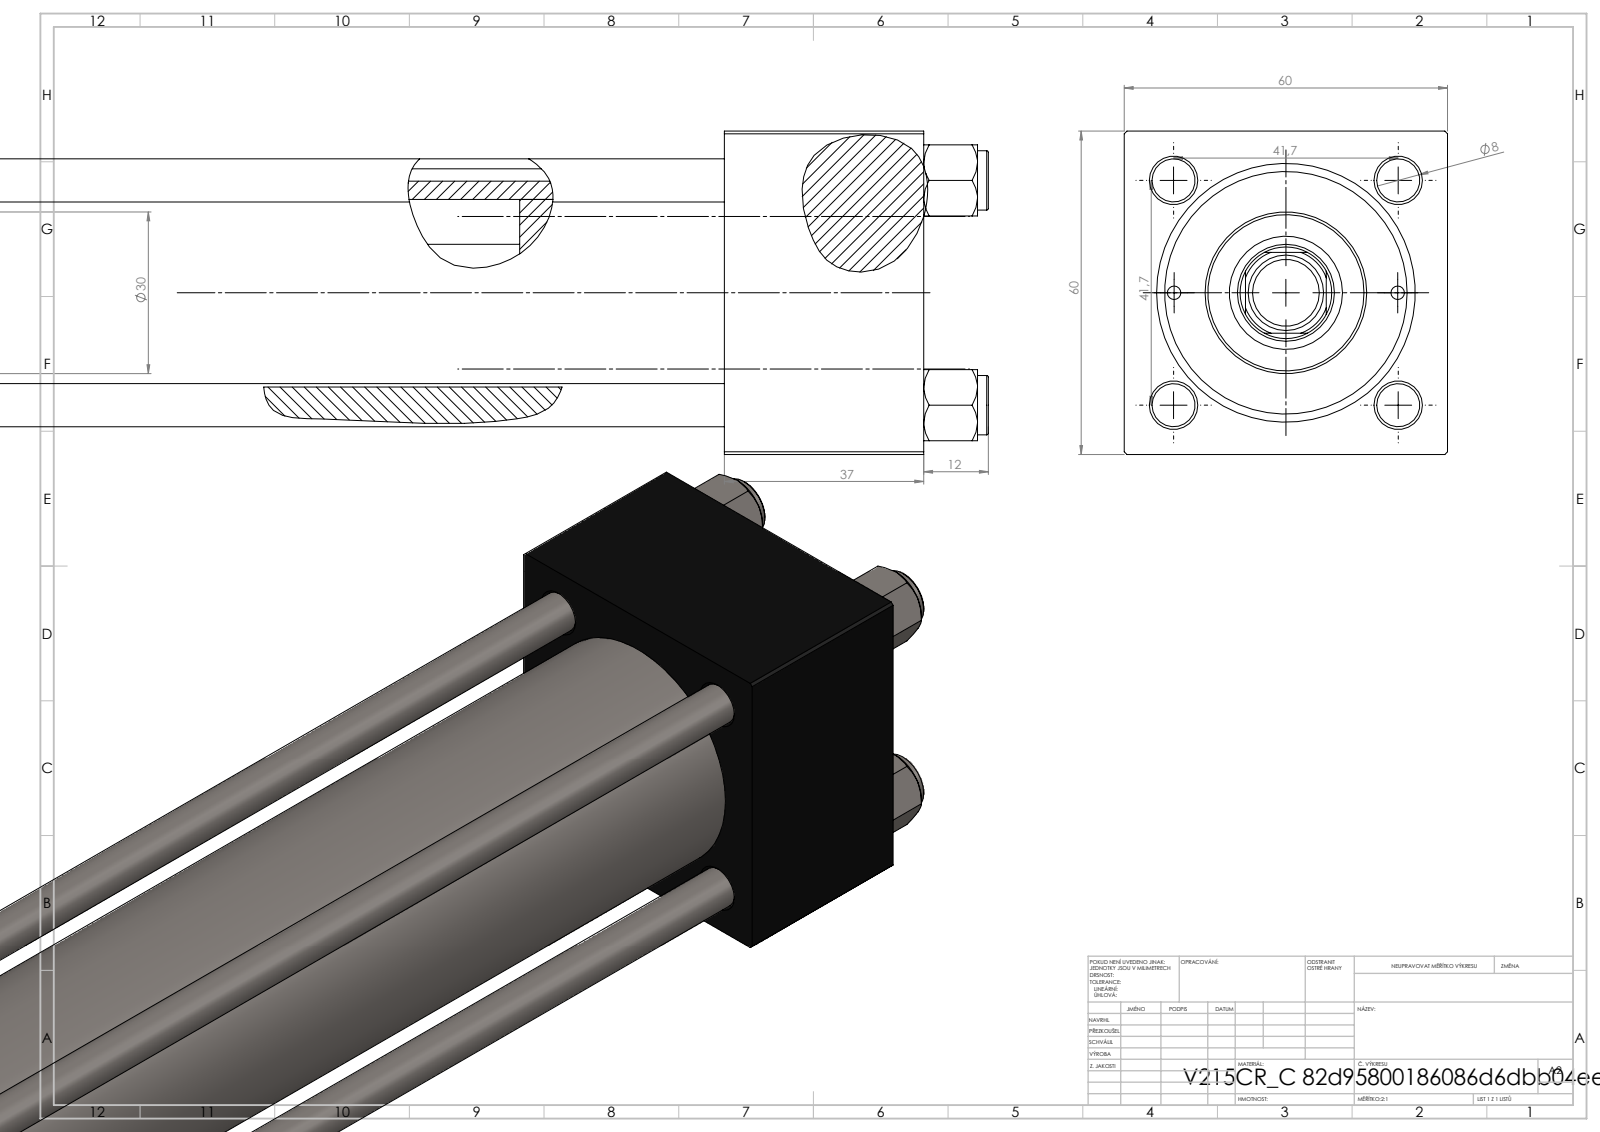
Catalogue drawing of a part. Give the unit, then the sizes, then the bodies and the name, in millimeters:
Units: millimetres
Overall size (bounding box): 483 × 60 × 60
Round holes (diameter × count): ⌀8 ×4, ⌀2.5 ×2, ⌀7 ×2, ⌀16.66 ×2, ⌀24 ×2, ⌀8.5 ×1, ⌀18 ×1, ⌀21 ×1, ⌀31 ×1, ⌀40 ×1, ⌀45 ×1
Round bosses / shafts (diameter × count): ⌀11 ×4, ⌀46 ×1, ⌀30 ×1, ⌀14 ×1, ⌀12 ×1
Partial cylindrical surfaces — rounded edges, fillets, slot ends (radius × count): R8.5 ×1
Main face-to-face distances: 60, 37, 428, 391, 53, 375, 338, 399.3, 362.3, 24.3
Hole centre spacings: 20.85, 29.49, 41.7, 46.53, 20.75, 58.97, 41.5, 372.5
Volume: 646 215 mm³ · Surface area: 226 166 mm²
Bodies: 12 solids, 1168 faces (532 planar, 94 cylindrical, 542 other)
Part name (STEP PRODUCT): NUT_M5_C; V215CR_C_TYCINKA; V215CR_C_Body; V215_VC_A (+2 more)
STEP written by: SolidWorks 2019 (CONFIG_CONTROL_DESIGN)
